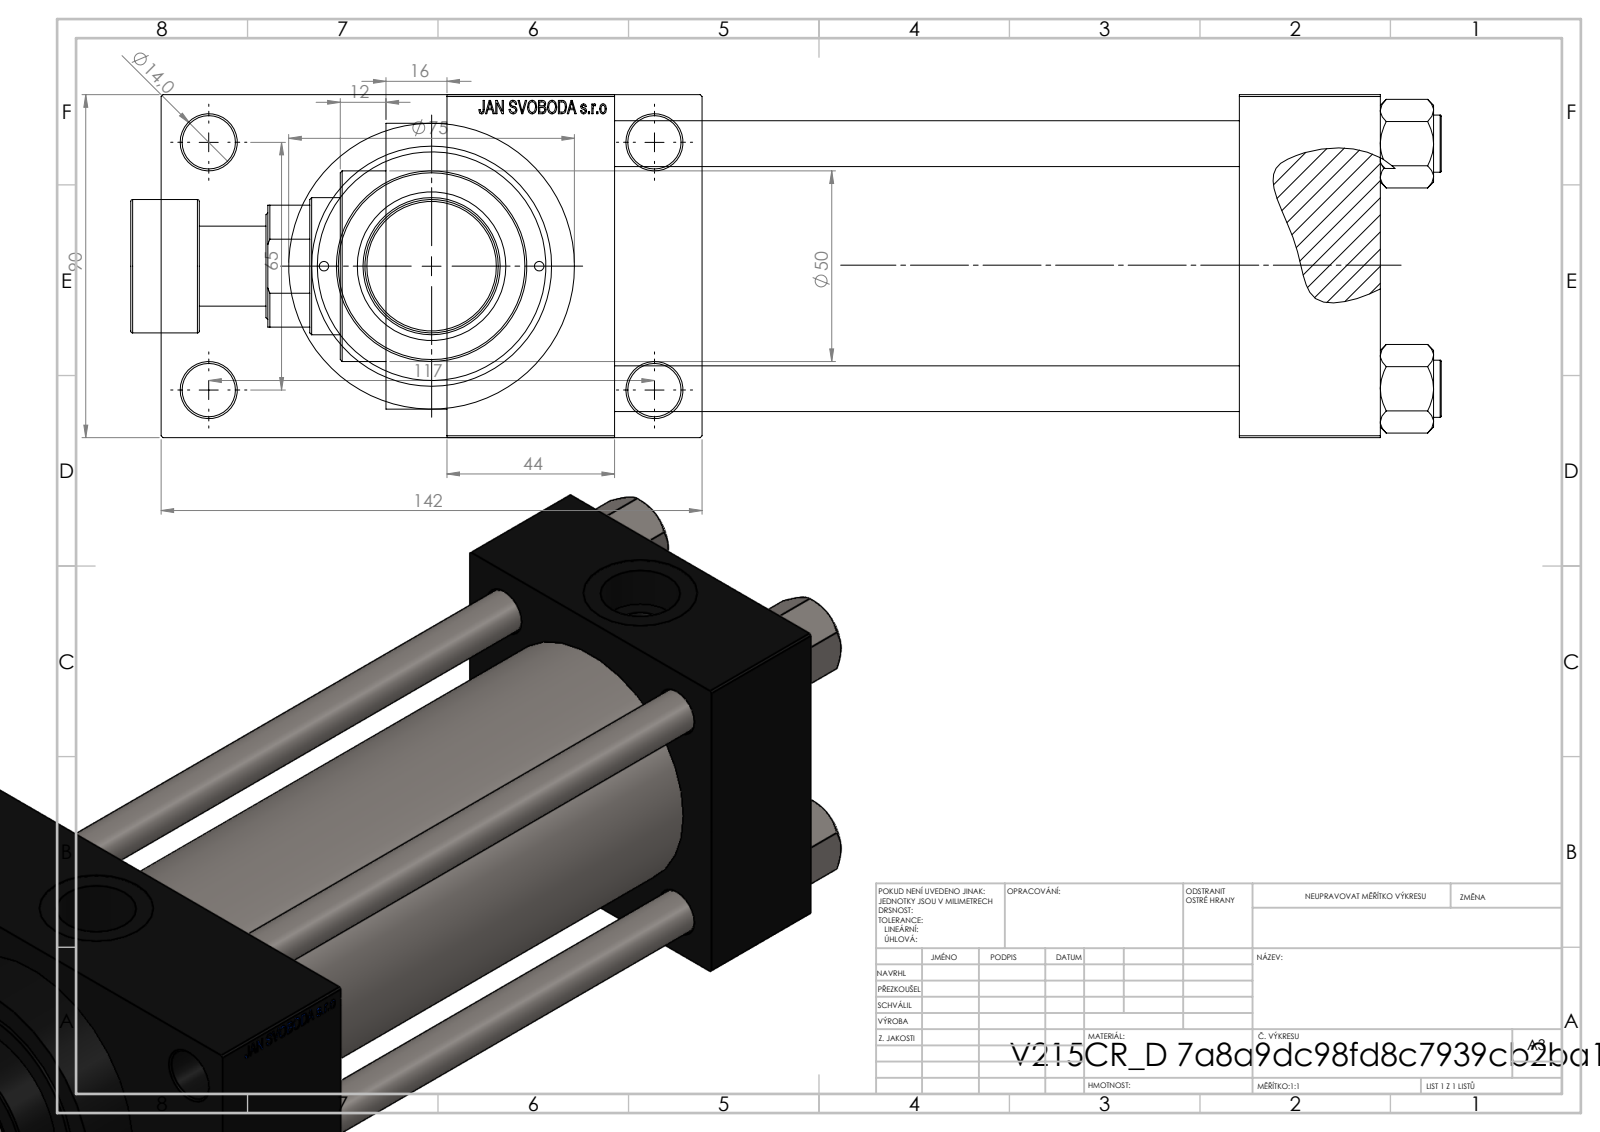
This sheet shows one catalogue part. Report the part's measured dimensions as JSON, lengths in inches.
{"part_name": "NUT_M5_D; V215CR_D_TYCINKA; V215CR_VCP_D; V215CR_ROD_END_F (+2 more)", "step_written_by": "SolidWorks 2019 (CONFIG_CONTROL_DESIGN)", "units": "inches", "bodies": {"solids": 12, "faces": 1126, "planar": 503, "cylindrical": 97, "other": 526}, "overall_size": [13.543, 5.591, 3.543], "volume_in3": 83.24, "surface_area_in2": 435.3, "round_holes": [[0.472, 4], [0.551, 4], [0.098, 2], [0.276, 2], [0.825, 2], [1.181, 2], [1.004, 1], [1.417, 1], [1.535, 1], [1.969, 1], [2.362, 1], [2.48, 1]], "round_bosses_or_shafts": [[0.591, 4], [2.953, 1], [2.717, 1], [1.378, 1], [0.827, 1]], "face_to_face_distances": [3.543, 6.457, 1.457, 7.913, 9.646, 8.189, 1.732, 1.024, 4.567, 5.591], "hole_center_spacings": [1.037, 1.275, 1.748, 1.79, 2.531, 2.635, 2.694, 2.748]}
